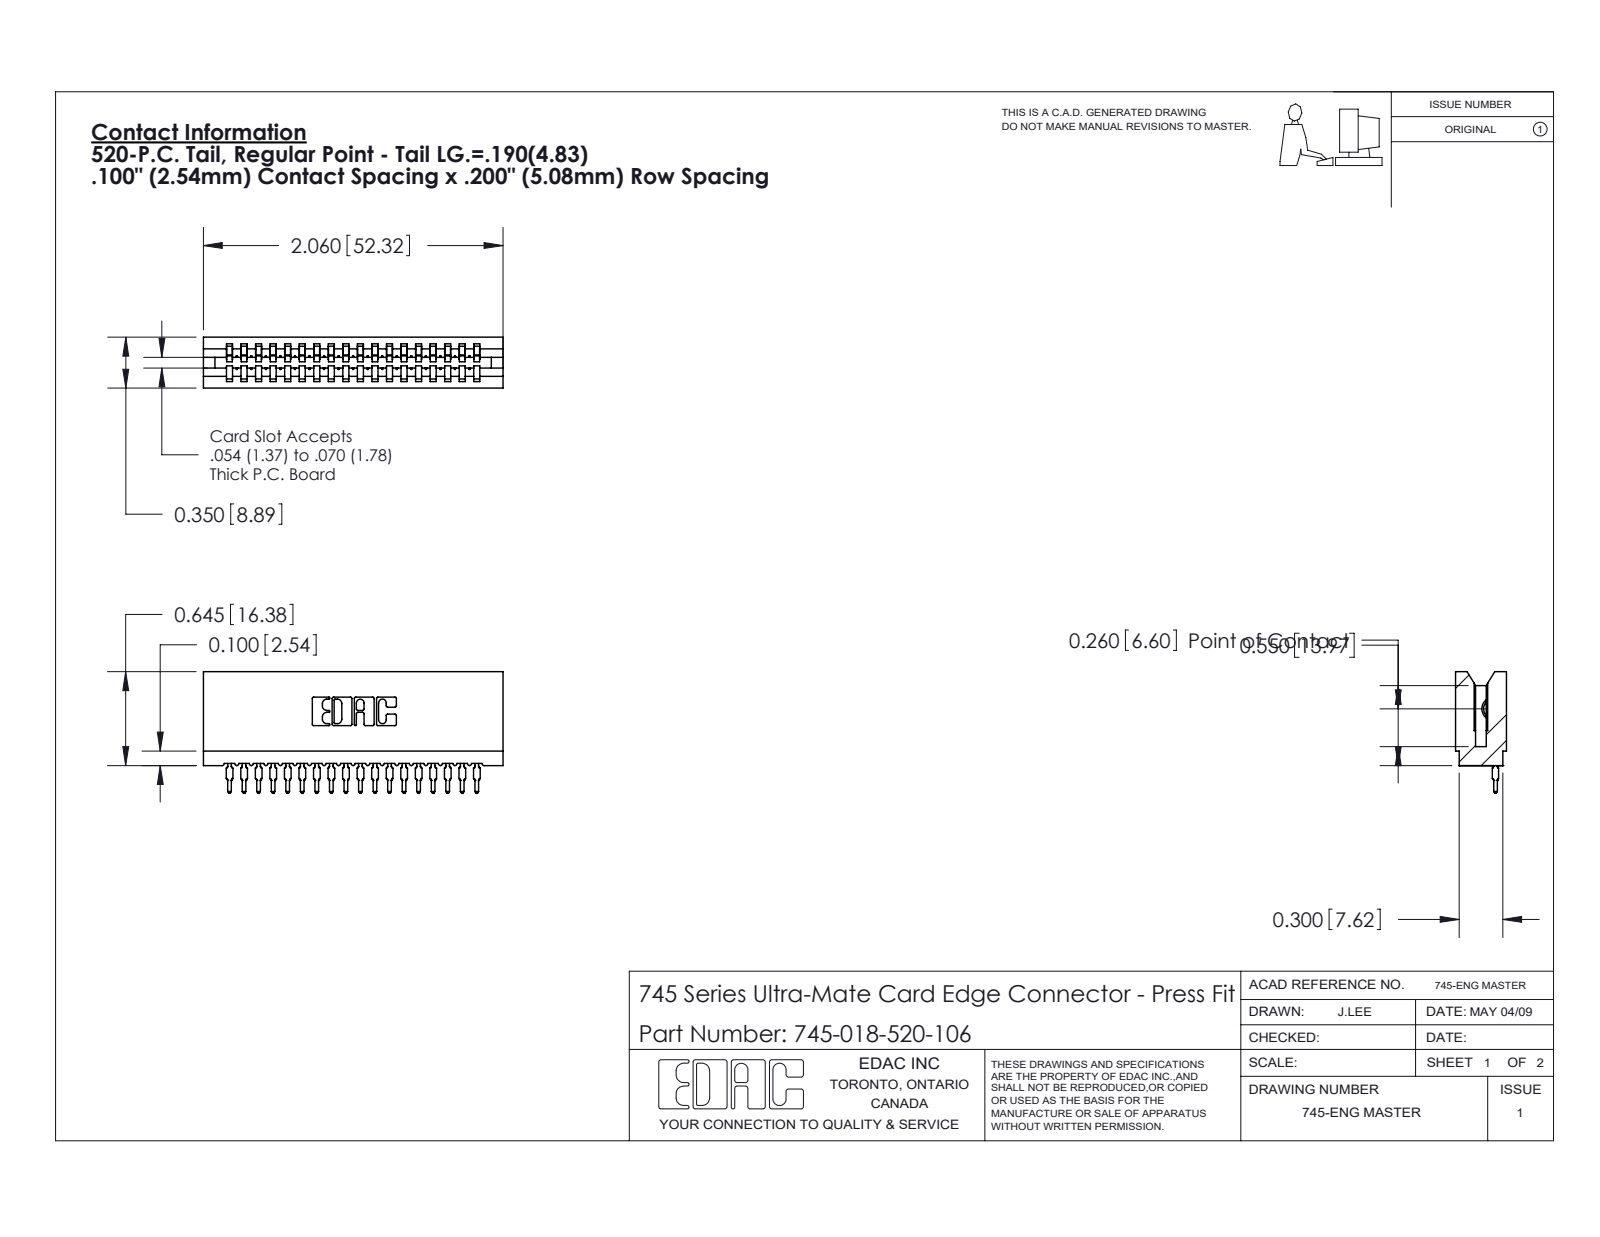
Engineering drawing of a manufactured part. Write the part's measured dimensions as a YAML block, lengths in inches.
part_name: "745-292-001_520; 745 Part_Insulator Option - 06; 745-018-520-106"
step_written_by: "SolidWorks 2020 (CONFIG_CONTROL_DESIGN)"
units: inches
bodies: {solids: 19, faces: 2112, planar: 1262, cylindrical: 382, other: 468}
overall_size: [2.06, 0.836, 0.35]
volume: 0.283
surface_area: 12.55
partial_cylinders:
  - {radius: 0.015, count: 36}
  - {radius: 0.021, count: 36}
  - {radius: 0.01, count: 22}
  - {radius: 0.007, count: 6}
  - {radius: 0.031, count: 6}
  - {radius: 0.005, count: 4}
  - {radius: 0.011, count: 4}
  - {radius: 0.026, count: 3}
face_to_face_distances: [0.1, 0.2, 0.3, 0.4, 0.5, 0.6, 0.35, 0.7, 0.8, 0.138]
